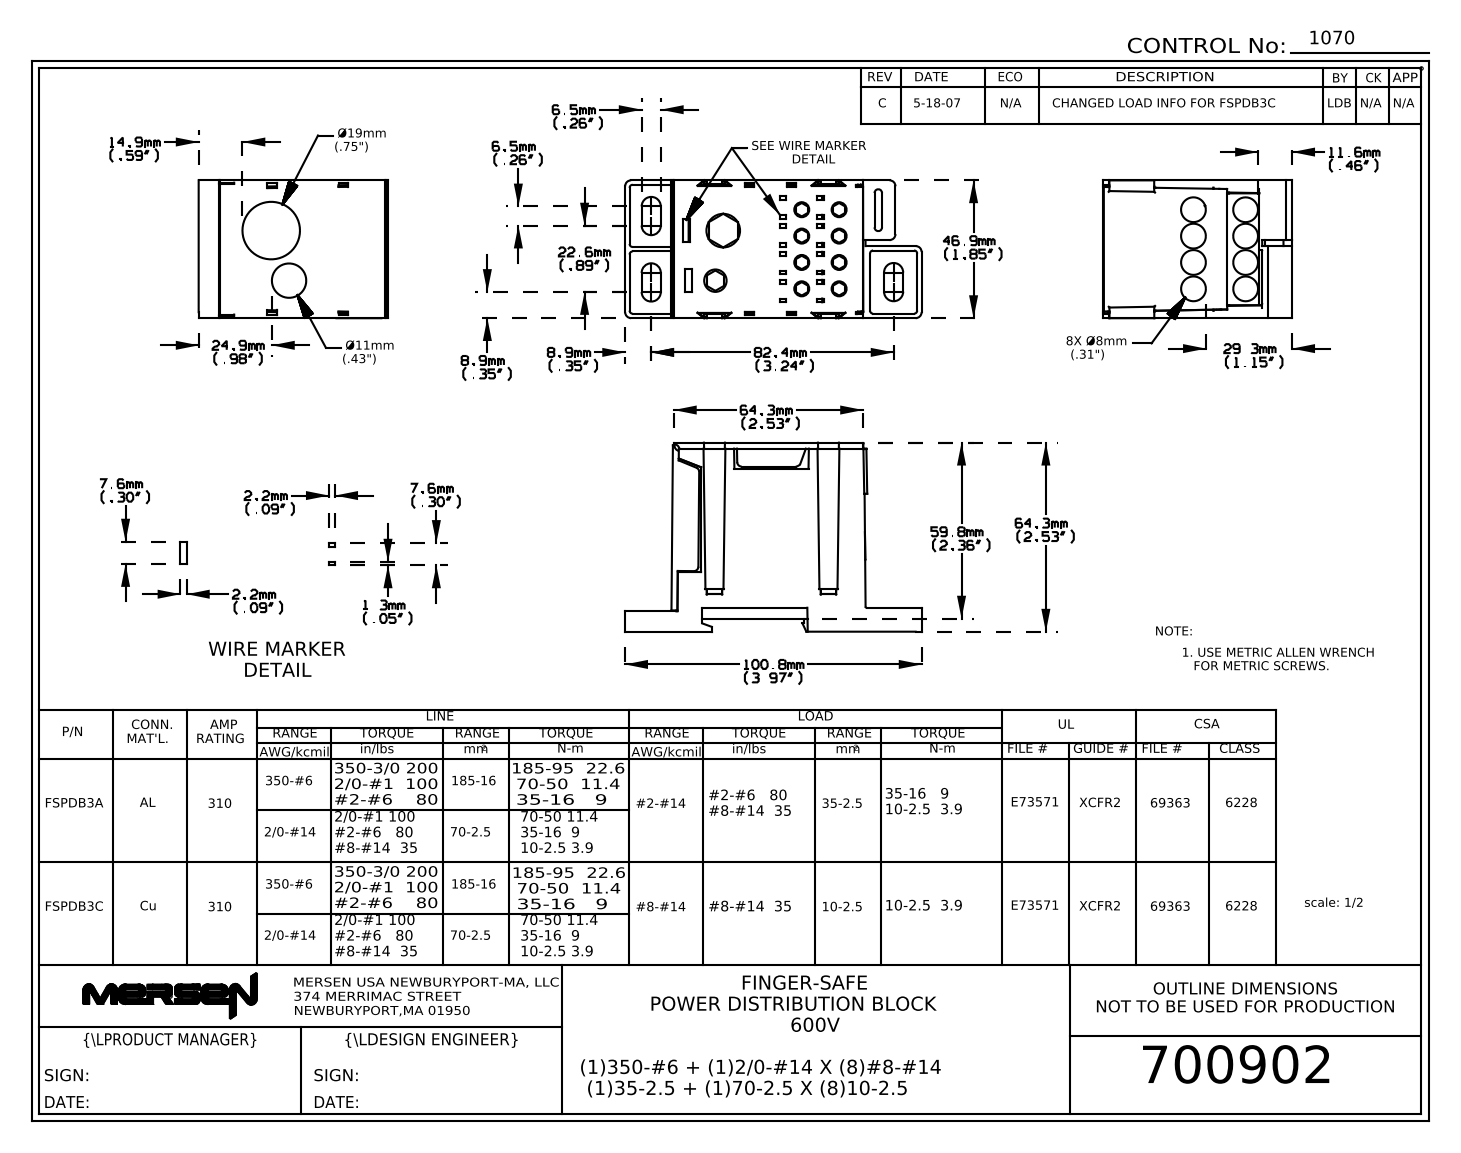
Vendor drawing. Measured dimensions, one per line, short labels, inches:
name: 700902revc
written by: SolidWorks 2012 (AUTOMOTIVE_DESIGN)
unit: in
bodies: 4 solids, 614 faces (424 planar, 188 cylindrical, 2 other)
size: 3.969 × 2.53 × 1.845
volume: 2.826 in³; area: 78.52 in²
holes: 8× ⌀0.2, 8× ⌀0.332, 2× ⌀0.173, 1× ⌀0.3, 1× ⌀0.45, 1× ⌀0.465, 1× ⌀0.775
rounds: 22× R0.01, 17× R0.015, 15× R0.05, 12× R0.025, 12× R0.04, 10× R0.03, 8× R0.08, 6× R0.128
face distances: 0.08, 2.13, 1.845, 2.492, 2.45, 0.32, 2.53, 2.05, 0.4, 0.061
hole spacings: 0.353, 0.706, 0.5, 0.353, 0.612, 0.68, 0.767, 0.98
